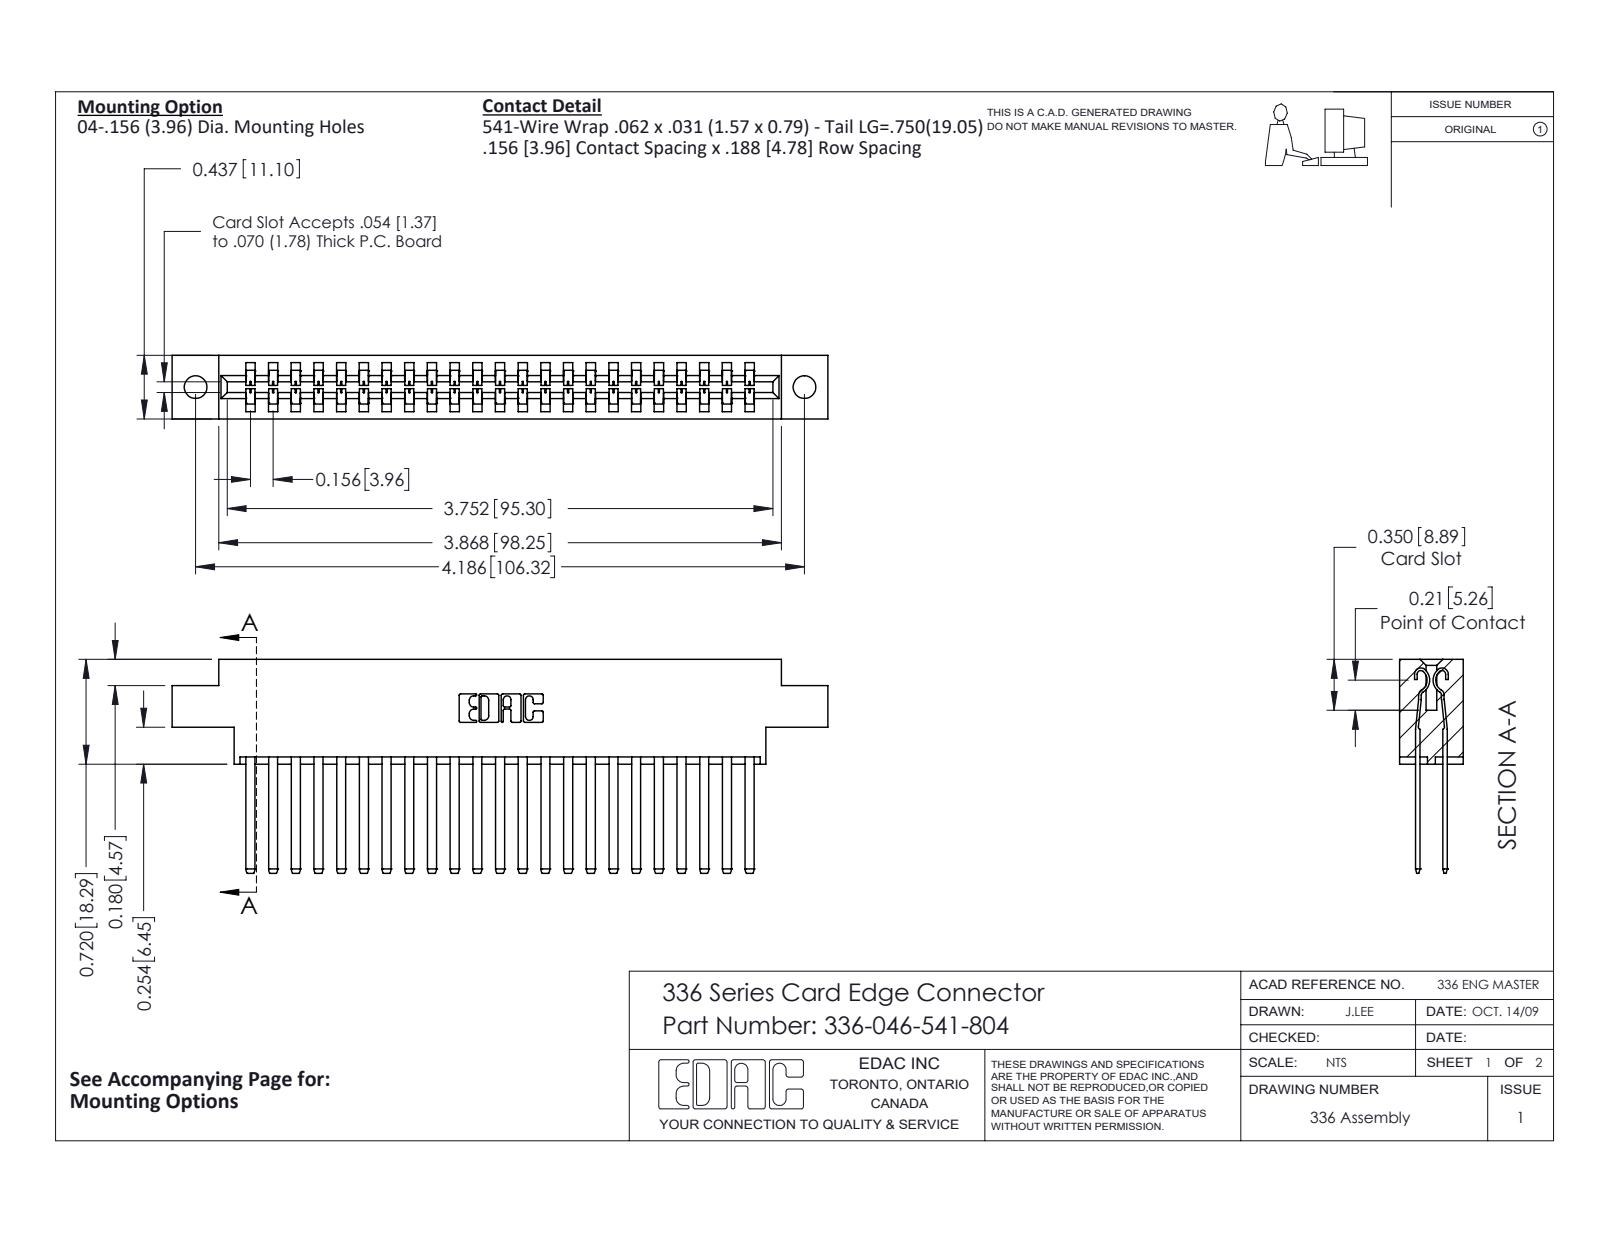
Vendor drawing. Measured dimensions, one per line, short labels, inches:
name: 336 Part_Offset - .156 Dia - TH; 336-046-541-804; 336-290-001_336-290-541
written by: SolidWorks 2020 (CONFIG_CONTROL_DESIGN)
unit: in
bodies: 47 solids, 2050 faces (1270 planar, 780 cylindrical, 0 other)
size: 4.509 × 1.47 × 0.437
volume: 1.036 in³; area: 32.9 in²
holes: 2× ⌀0.156
rounds: 92× R0.004, 46× R0.056, 22× R0.01, 6× R0.007, 6× R0.031, 4× R0.022, 4× R0.04, 3× R0.026
face distances: 0.188, 0.328, 0.14, 0.297, 0.109, 0.031, 0.437, 0.033, 0.156, 0.181
hole spacings: 4.186
